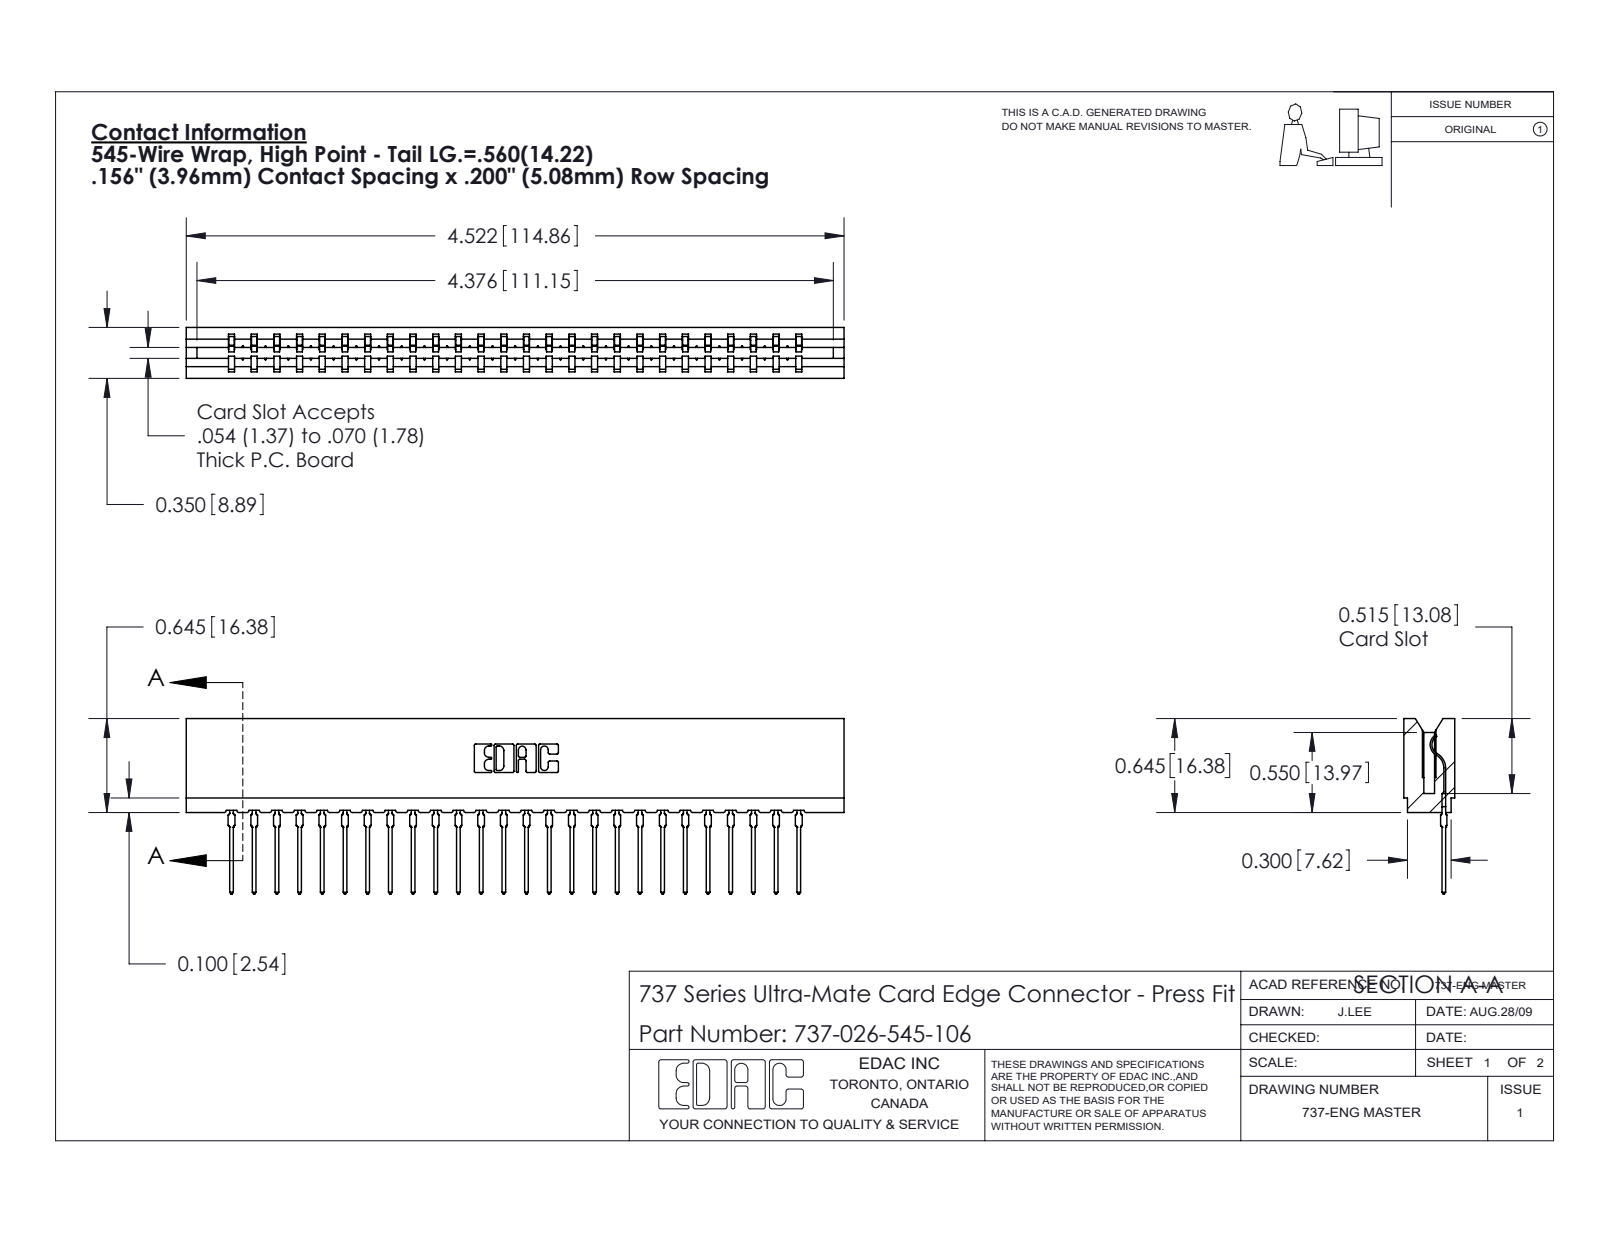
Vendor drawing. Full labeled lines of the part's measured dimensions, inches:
Part name (STEP PRODUCT): 737-026-545-106; 737 Part_Insulator Option - 06; 745-292-001_545
STEP written by: SolidWorks 2020 (CONFIG_CONTROL_DESIGN)
Units: inches
Bodies: 27 solids, 3033 faces (1823 planar, 534 cylindrical, 676 other)
Overall size (bounding box): 4.522 × 1.206 × 0.35
Volume: 0.688 in³ · Surface area: 23.67 in²
Partial cylindrical surfaces — rounded edges, fillets, slot ends (radius × count): R0.015 ×52, R0.021 ×52, R0.01 ×22, R0.007 ×6, R0.031 ×6, R0.005 ×4, R0.011 ×4, R0.026 ×3
Main face-to-face distances: 0.138, 0.212, 0.35, 0.624, 0.074, 0.156, 0.045, 0.305, 0.093, 0.167
